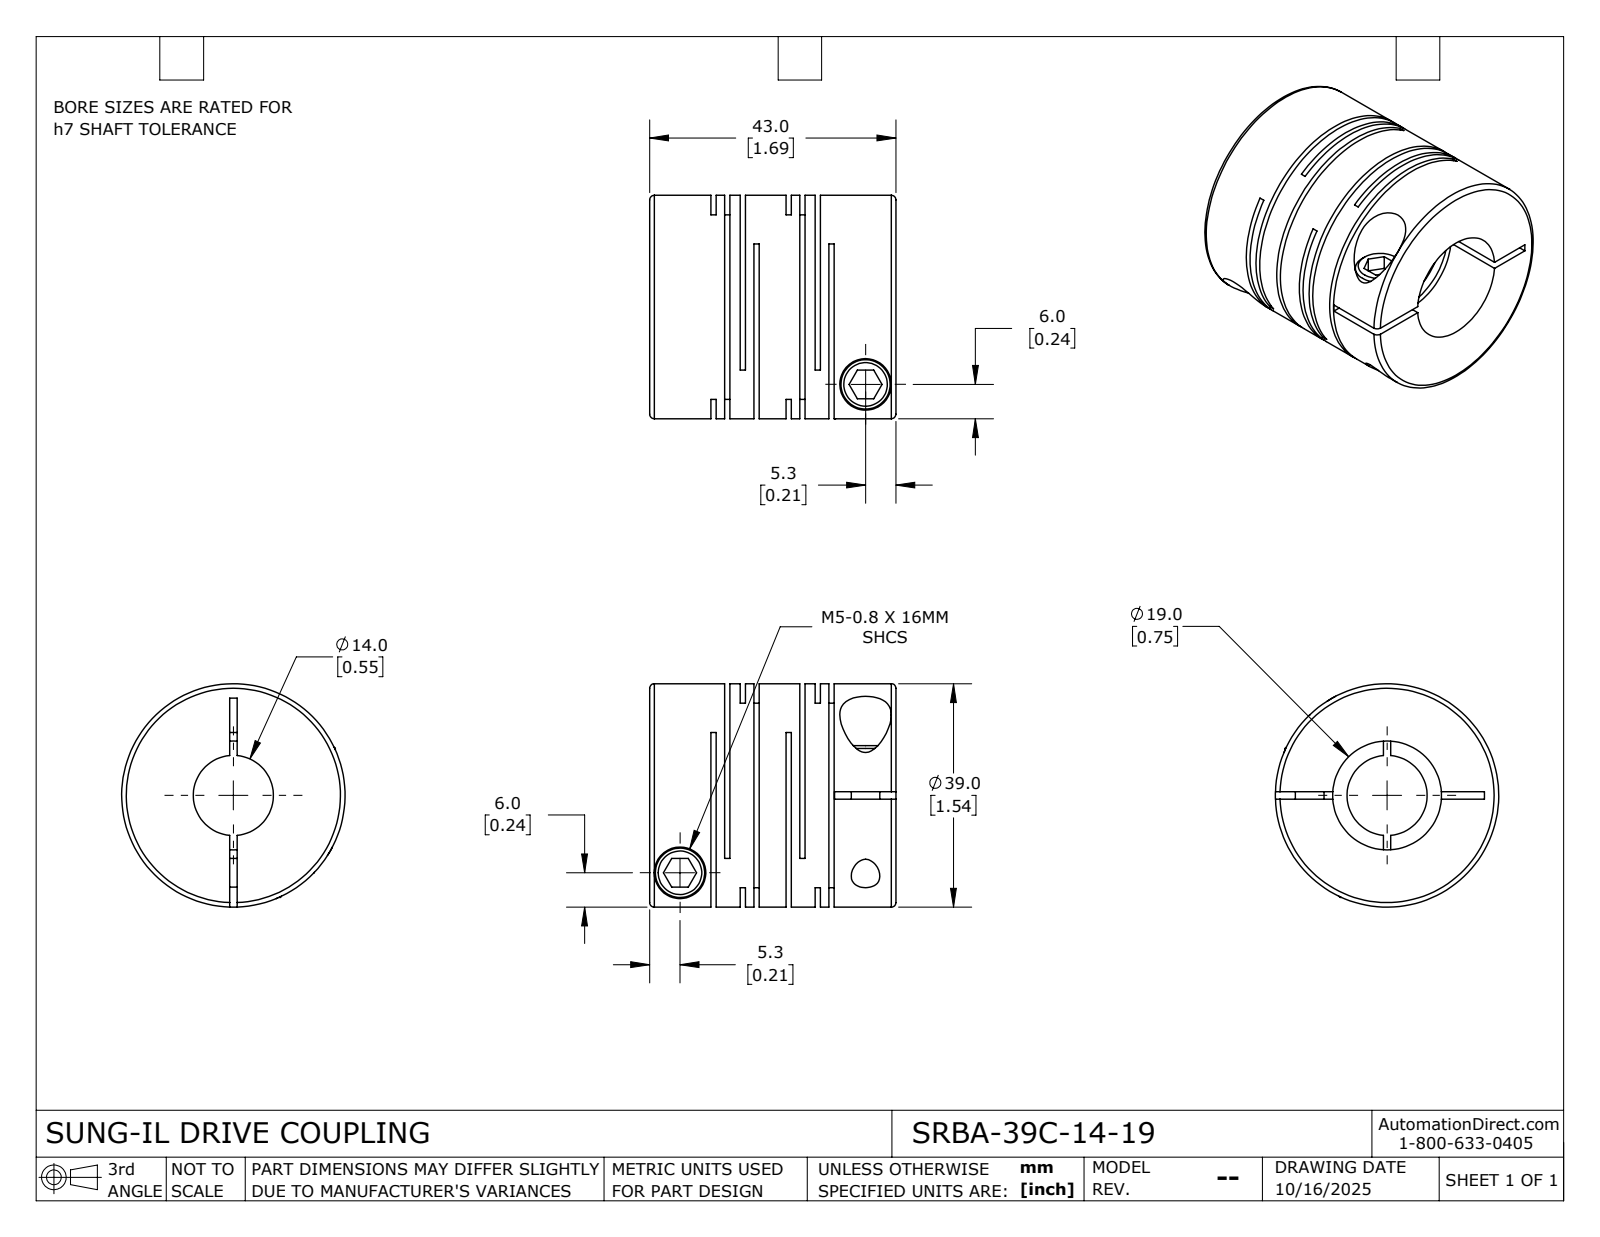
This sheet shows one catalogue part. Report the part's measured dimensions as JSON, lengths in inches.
{"part_name": "SRBA-39C-14-19", "step_written_by": "SolidWorks 2024 (CONFIG_CONTROL_DESIGN)", "units": "inches", "bodies": {"solids": 1, "faces": 115, "planar": 60, "cylindrical": 42, "other": 13}, "overall_size": [1.693, 1.535, 1.535], "volume_in3": 2.064, "surface_area_in2": 33.89, "round_holes": [[0.197, 2], [0.354, 2], [0.551, 1], [0.748, 1]], "round_bosses_or_shafts": [[0.339, 2], [1.535, 1]], "face_to_face_distances": [0.516, 0.036, 0.094, 0.201, 0.421, 0.552, 0.717, 0.48, 0.131, 0.295]}
